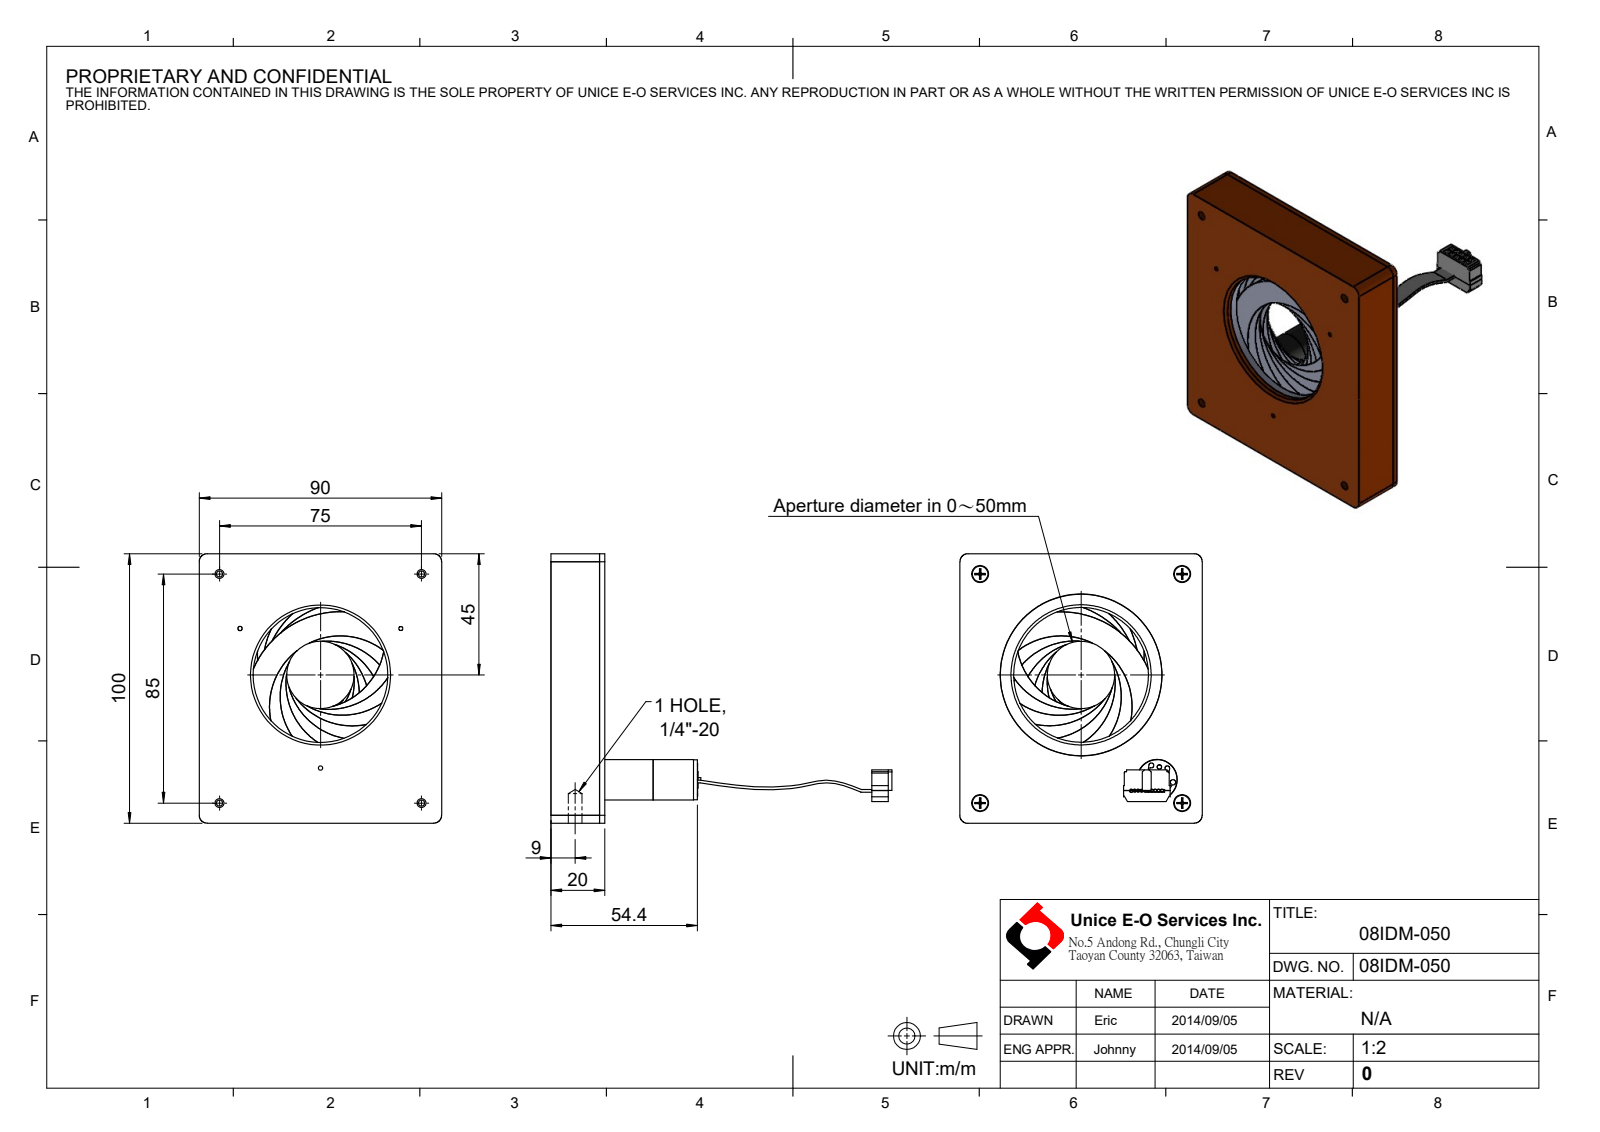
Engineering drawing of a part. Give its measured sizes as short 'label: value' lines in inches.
name: 08IDM-050
written by: SolidWorks 2016 (CONFIG_CONTROL_DESIGN)
unit: in
bodies: 41 solids, 1691 faces (857 planar, 776 cylindrical, 58 other)
size: 4.984 × 3.937 × 3.543
volume: 7.766 in³; area: 120.5 in²
holes: 8× ⌀0.083, 5× ⌀0.063, 5× ⌀0.098, 4× ⌀0.13, 4× ⌀0.134, 3× ⌀0.118, 2× ⌀0.043, 2× ⌀0.054, 2× ⌀0.058, 2× ⌀0.059, 2× ⌀0.094, 1× ⌀0.067
bosses: 8× ⌀0.071, 4× ⌀0.228, 4× ⌀0.118, 1× ⌀2.839, 1× ⌀2.835, 1× ⌀2.559, 1× ⌀0.591, 1× ⌀0.583
rounds: 160× R0.024, 30× R0.028, 15× R1.033, 15× R1.034, 10× R0.019, 10× R0.025, 5× R1.385, 5× R1.386
face distances: 0.079, 0.709, 0.787, 0.331, 0.252, 0.102, 0.606, 0.685, 0.354, 0.236
hole spacings: 1.145, 0.217, 0.306, 0.447, 0.876, 0.877, 1.273, 1.358
